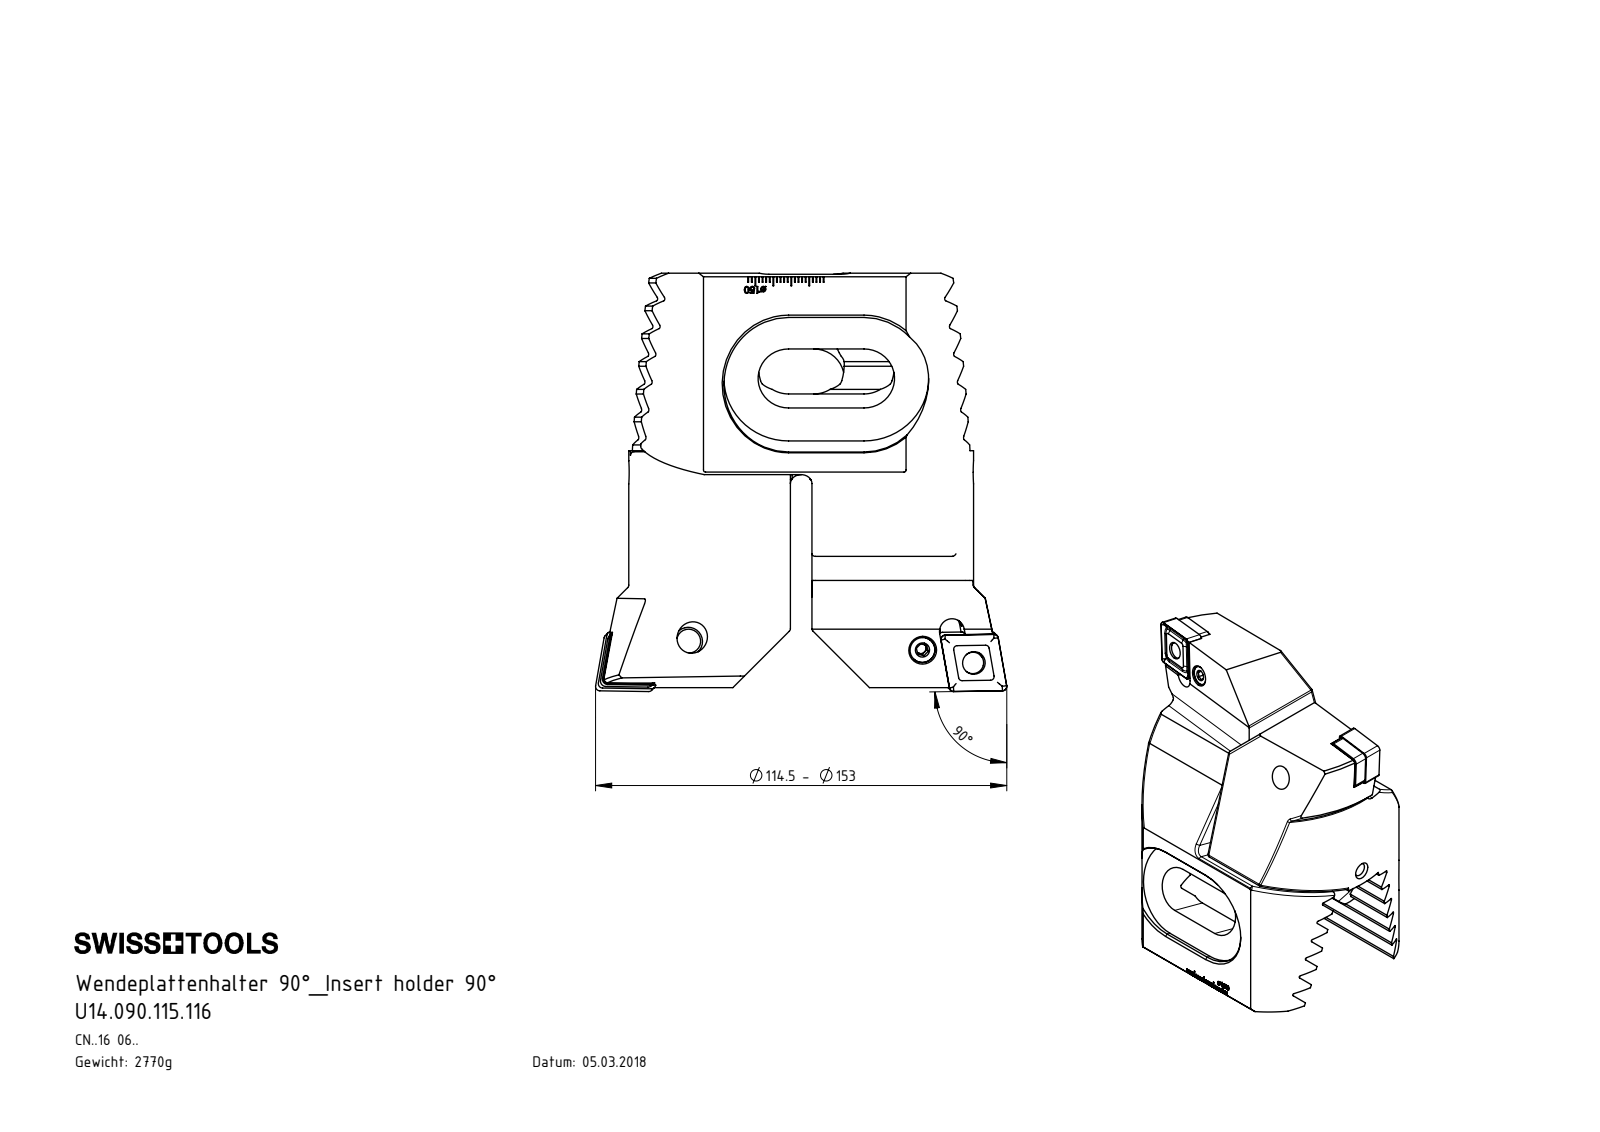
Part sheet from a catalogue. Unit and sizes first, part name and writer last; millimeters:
Units: millimetres
Overall size (bounding box): 116.42 × 114.5 × 75.2
Round holes (diameter × count): ⌀2 ×2, ⌀6.35 ×2, ⌀7 ×2, ⌀8.05 ×2, ⌀8.4 ×2, ⌀5 ×1
Round bosses / shafts (diameter × count): ⌀6 ×3, ⌀8 ×2, ⌀7.9 ×2, ⌀6.4 ×2, ⌀3.55 ×2, ⌀4 ×1
Partial cylindrical surfaces — rounded edges, fillets, slot ends (radius × count): R1 ×16, R0.58 ×12, R1.2 ×8, R1.5 ×8, R3 ×6, R3.5 ×6, R0.3 ×4, R8.5 ×4
Main face-to-face distances: 6.93, 13.86, 20.79, 27.71, 13.19, 6, 20.78, 1.59, 13.85, 27.72
Hole centre spacings: 14.76, 15, 25, 48.3
Volume: 352 866 mm³ · Surface area: 70 305 mm²
Bodies: 14 solids, 864 faces (534 planar, 124 cylindrical, 206 other)
Part name (STEP PRODUCT): CNMG160612; Z94-xxx.001.067_C_CN16; WCE-ER3.101.000_A; WCE-ER2.101.004_A (+5 more)
STEP written by: SolidWorks 2017 (AUTOMOTIVE_DESIGN)
